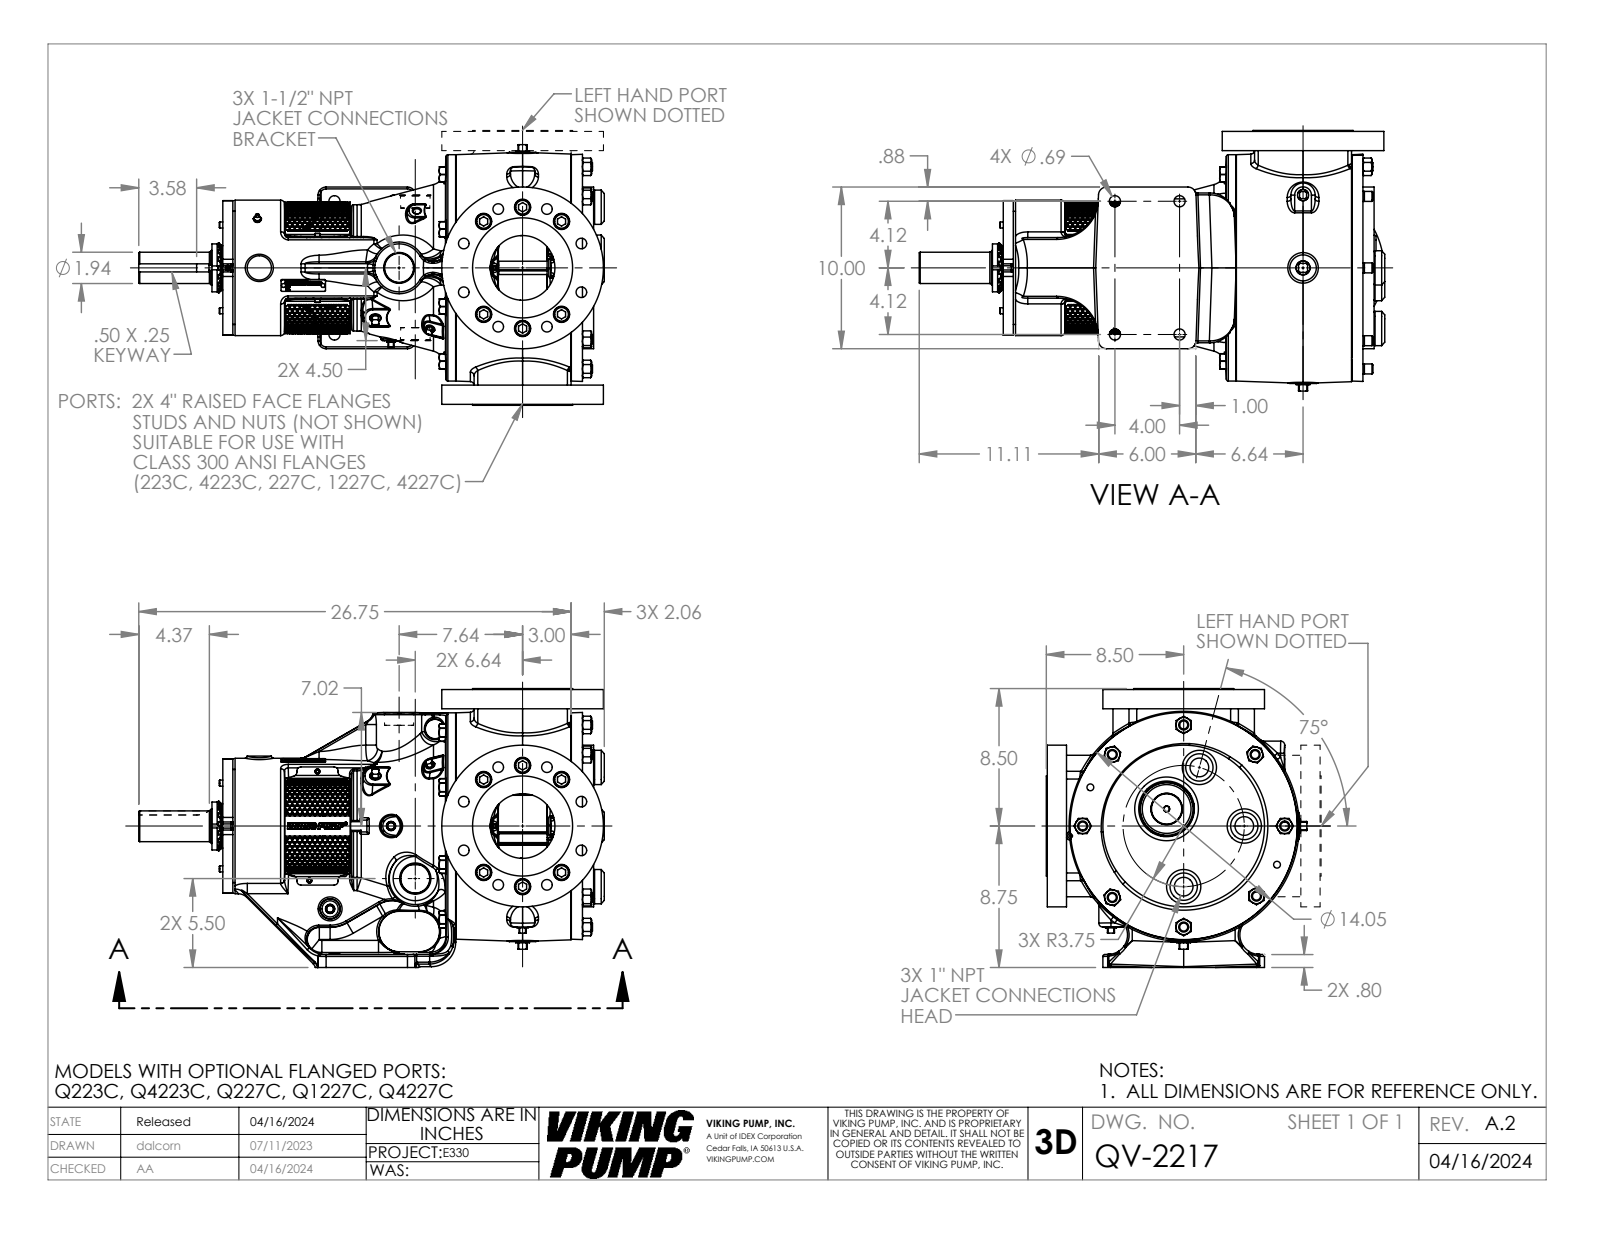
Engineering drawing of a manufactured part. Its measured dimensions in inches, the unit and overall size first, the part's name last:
Units: inches
Overall size (bounding box): 28.804 × 17.25 × 16.121
Round holes (diameter × count): ⌀0.656 ×28, ⌀1 ×12, ⌀0.25 ×9, ⌀0.266 ×8, ⌀1.157 ×8, ⌀0.688 ×4, ⌀1.156 ×3, ⌀1.85 ×3, ⌀0.159 ×2, ⌀0.313 ×2, ⌀0.33 ×2, ⌀0.422 ×2
Round bosses / shafts (diameter × count): ⌀0.937 ×12, ⌀0.625 ×11, ⌀0.617 ×8, ⌀10 ×3, ⌀2.12 ×3, ⌀1.75 ×3, ⌀0.312 ×3, ⌀0.19 ×3
Partial cylindrical surfaces — rounded edges, fillets, slot ends (radius × count): R0.12 ×52, R0.015 ×18, R0.092 ×18, R0.25 ×18, R0.07 ×16, R0.75 ×16, R0.5 ×14, R0.24 ×10
Main face-to-face distances: 1.19, 0.691, 3.75, 16, 17.19, 0.06, 1.25, 22.254, 22.944, 18.504
Hole centre spacings: 3.75, 7.276, 2.079, 3.133, 3.937, 5.932, 8.43, 9.82
Volume: 2 428 in³ · Surface area: 2 210 in²
Bodies: 1 solid, 3861 faces (1374 planar, 718 cylindrical, 1769 other)
Part name (STEP PRODUCT): QV-2217
STEP written by: SolidWorks 2022 (AUTOMOTIVE_DESIGN)
